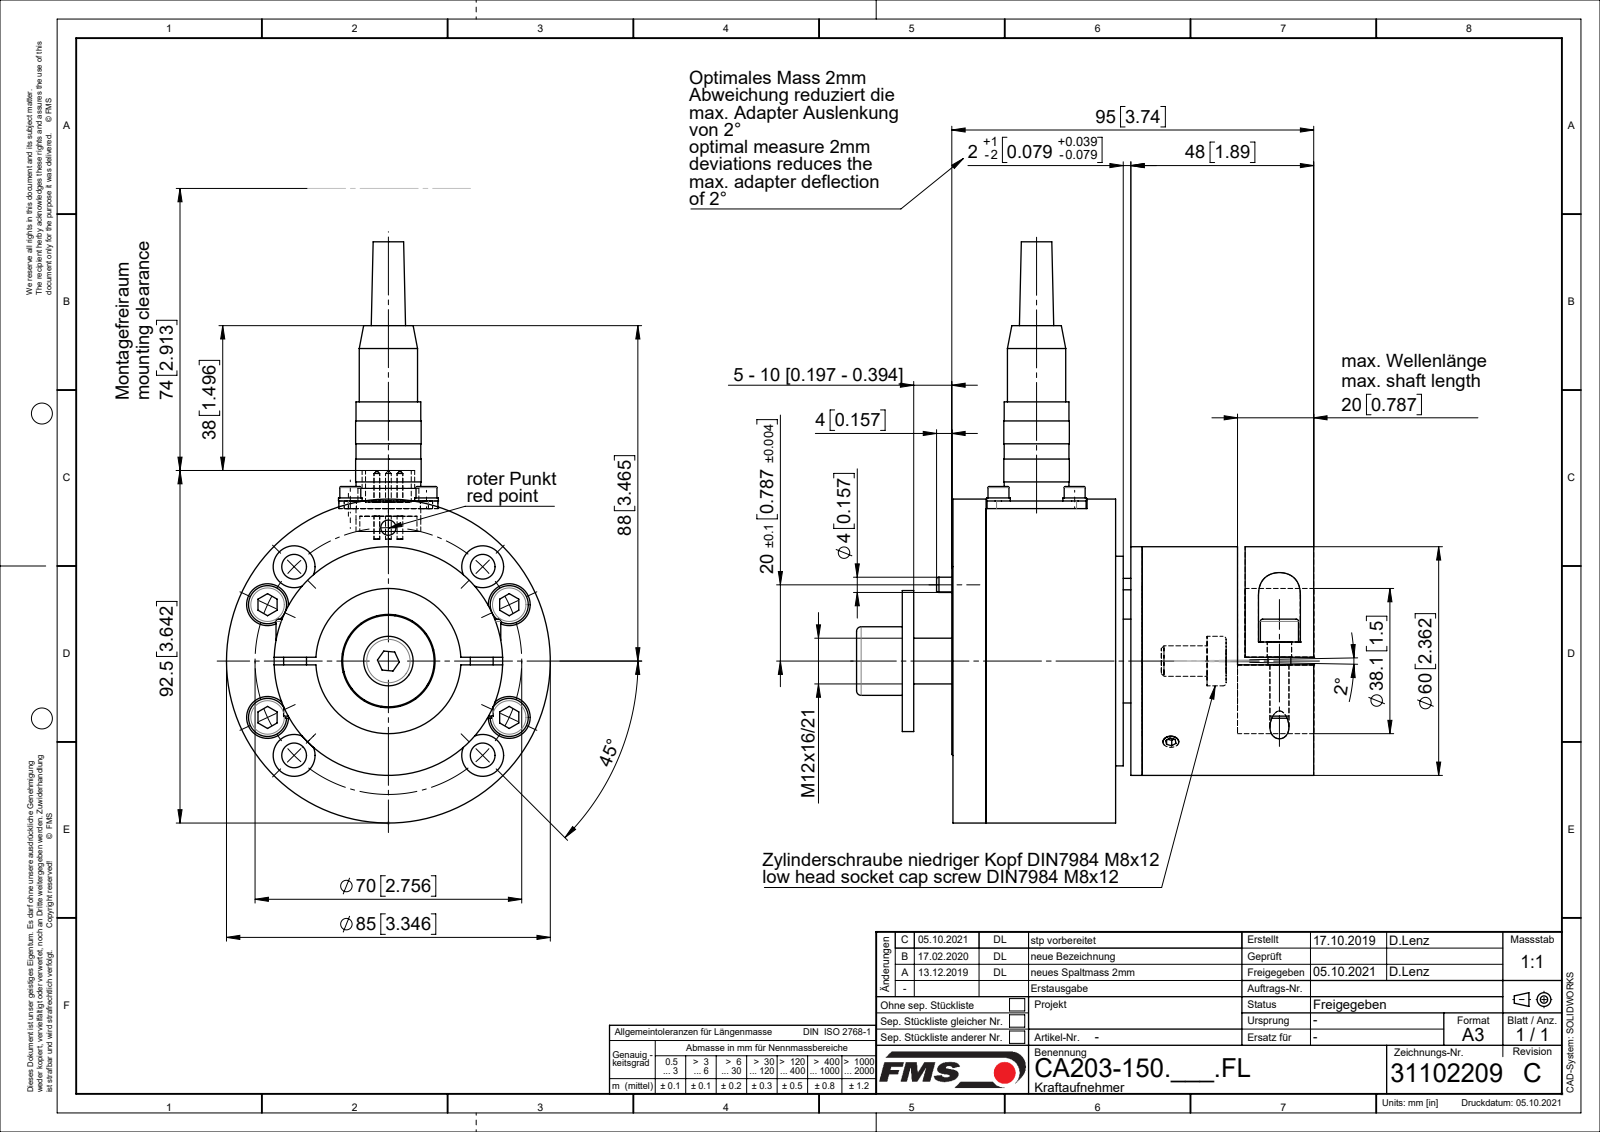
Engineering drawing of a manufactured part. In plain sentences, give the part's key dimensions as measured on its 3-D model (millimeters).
The part is named "070908-1_stp_01; 061205-3_01; Zyl-Schr DIN912_M3x6; Kabeldose_M14x1_Mini_5pol (+8 more)". Its 3-D file was written by "SolidWorks 2018 (CONFIG_CONTROL_DESIGN)". It is 43 solids with 785 faces: 270 planar, 326 cylindrical and 189 other. Overall it measures 152.5 by 120 by 85 millimeters. Its volume is 300 673 cubic millimeters and its surface area 111 415 square millimeters. Round holes: 8 of diameter 2.5, 8 of diameter 6.5, 8 of diameter 11, 6 of diameter 5, 5 of diameter 4, 4 of diameter 3.1, 4 of diameter 3.2, 4 of diameter 3.6, 4 of diameter 7, 2 of diameter 3, 2 of diameter 6.4, 1 of diameter 4.2. Round bosses or shafts: 8 of diameter 3, 7 of diameter 6, 6 of diameter 10, 5 of diameter 1.5, 4 of diameter 6.2, 4 of diameter 5.7, 4 of diameter 5.5, 1 of diameter 85. Partial cylindrical surfaces (rounded edges, fillets, slot ends): 4 of radius 2.5, 2 of radius 5, 2 of radius 5.5. The main face-to-face distances are 2, 41, 10, 30, 45, 3, 22, 60, 50, 34. The hole center spacings are 35, 20, 24.78, 25.2, 32.8, 51.14, 56.46, 28.28.
